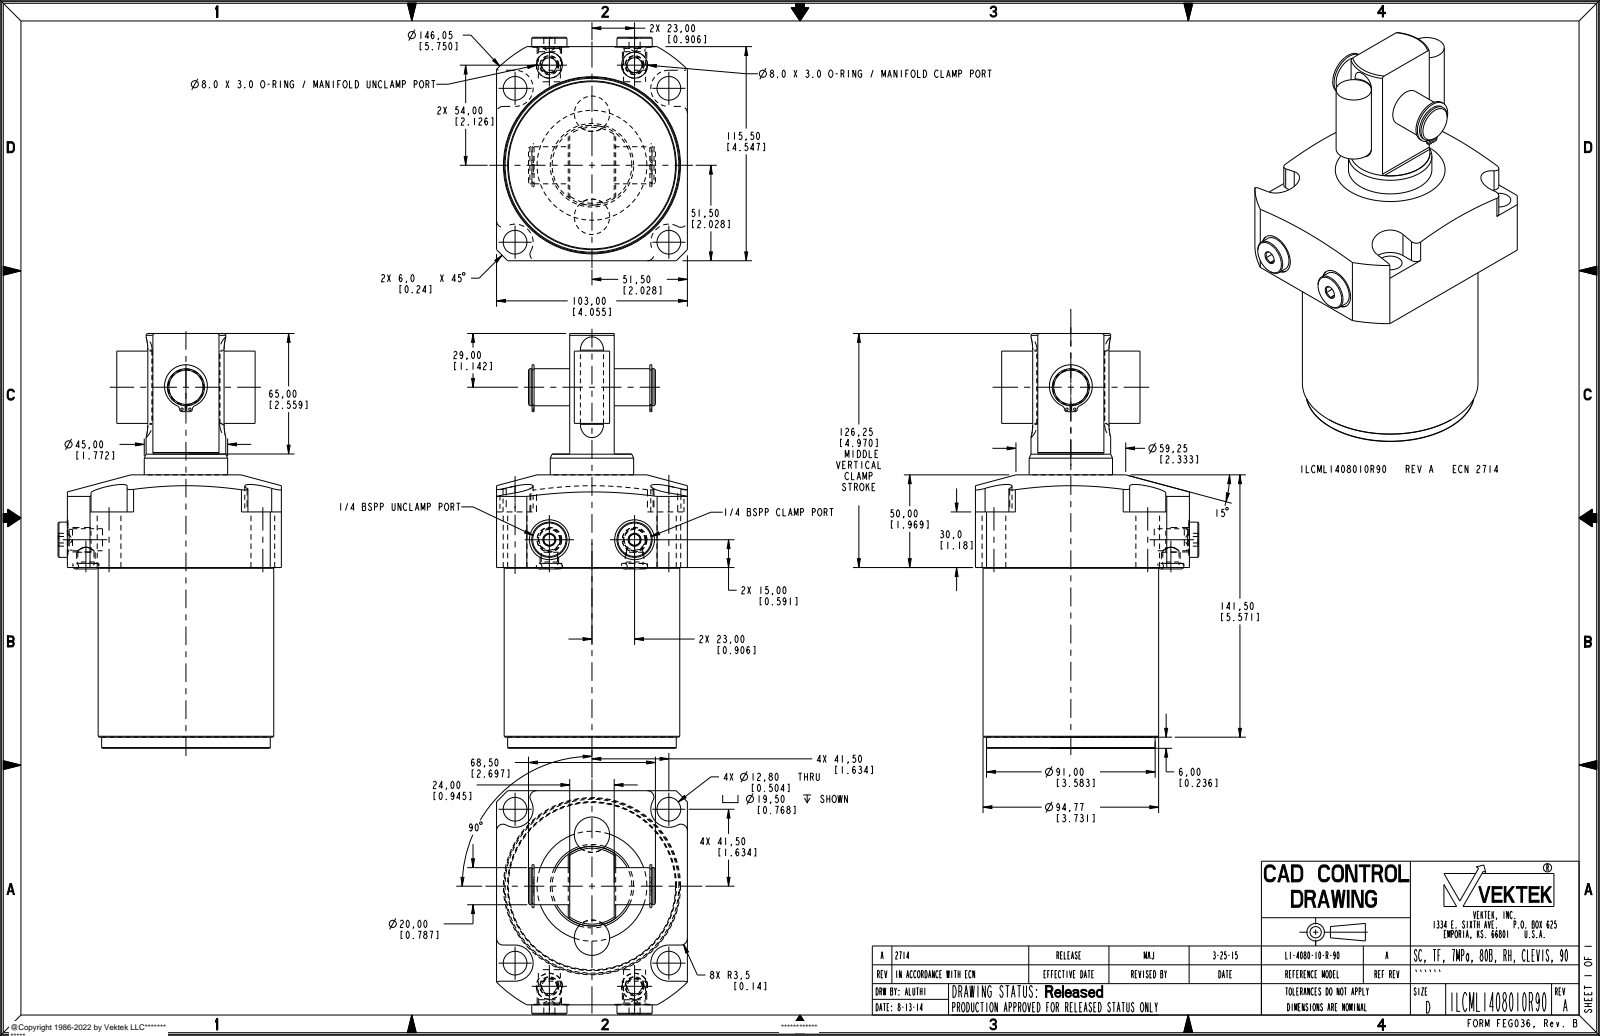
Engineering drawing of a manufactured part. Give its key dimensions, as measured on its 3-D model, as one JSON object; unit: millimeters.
{"part_name": "ILCML1408010R90", "step_written_by": "PRO/ENGINEER BY PARAMETRIC TECHNOLOGY CORPORATION, 2013320 (AUTOMOTIVE_DESIGN)", "units": "millimeters", "bodies": {"solids": 5, "faces": 239, "planar": 85, "cylindrical": 106, "other": 48}, "overall_size": [223.75, 120.55, 103], "volume_mm3": 1304000, "surface_area_mm2": 98861, "round_holes": [[12.8, 4], [1.32, 2], [6, 2], [8.75, 2], [11.89, 2], [14, 2], [21.5, 2], [19.5, 1]], "round_bosses_or_shafts": [[19.05, 2], [19, 2], [13.16, 2], [11.2, 2], [10, 2], [94.77, 1], [91, 1], [45, 1]], "partial_cylinders_radius": [[3.5, 8], [9.75, 4], [0.8, 2], [1.32, 2], [1.99, 2], [9.53, 2], [73.03, 1]], "face_to_face_distances": [39.5, 63.5, 103, 97.5, 115.5, 24, 147.5, 50, 223.75, 126.25], "hole_center_spacings": [83, 12.06, 22.33, 46, 65.7, 97.28, 115.24, 117.38]}
